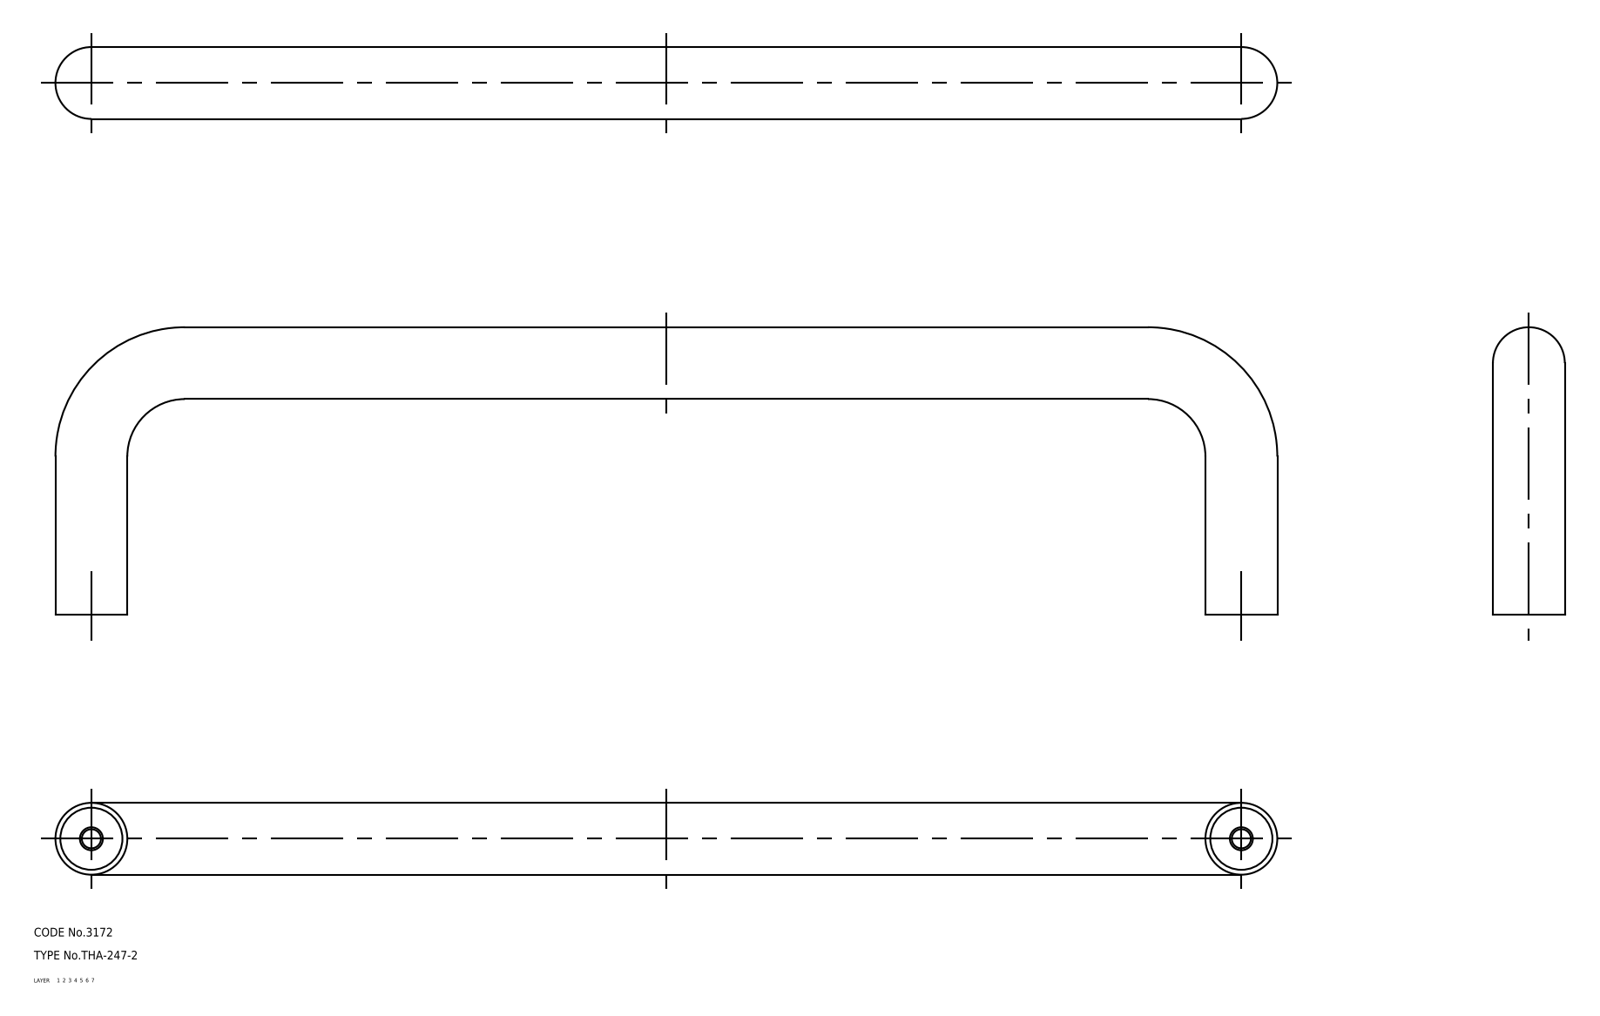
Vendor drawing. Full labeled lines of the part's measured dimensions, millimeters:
Part name (STEP PRODUCT): attachment; pull; THA_247_2_28097_36
STEP written by: CADfix (AUTOMOTIVE_DESIGN)
Units: millimetres
Bodies: 3 solids, 34 faces (0 planar, 0 cylindrical, 34 other)
Overall size (bounding box): 425 × 100 × 25
Volume: 79 519 mm³ · Surface area: 84 613 mm²
